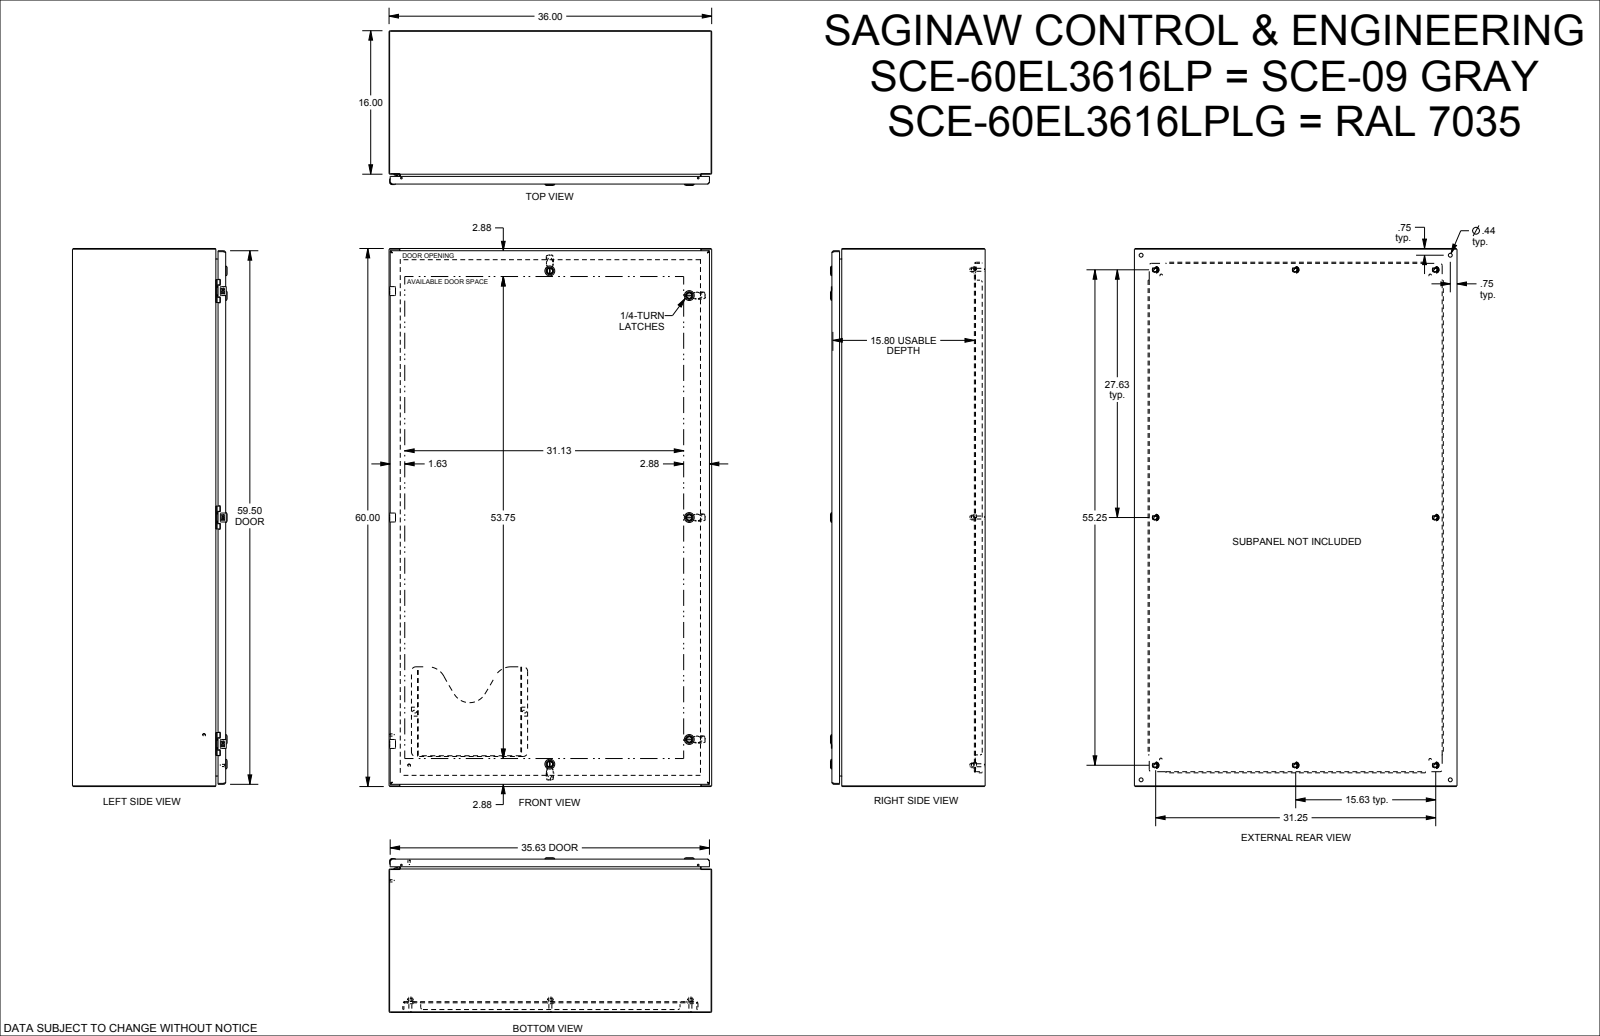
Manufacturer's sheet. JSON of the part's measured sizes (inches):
{"part_name": "SCE-60EL3616LP_REV2", "step_written_by": "SolidWorks 2021 (AUTOMOTIVE_DESIGN)", "units": "inches", "bodies": {"solids": 40, "faces": 2236, "planar": 1135, "cylindrical": 741, "other": 360}, "overall_size": [60, 36, 17.967], "volume_in3": 825.8, "surface_area_in2": 20194, "round_holes": [[0.5, 8], [0.172, 6], [0.205, 6], [0.244, 6], [0.375, 6], [0.197, 5], [0.394, 5], [0.634, 5], [0.281, 4], [0.437, 4], [0.04, 3], [0.218, 3]], "round_bosses_or_shafts": [[0.17, 9], [0.375, 8], [0.33, 8], [0.25, 6], [0.24, 6], [1.102, 5], [0.78, 5], [0.63, 5]], "partial_cylinders_radius": [[0.015, 28], [0.157, 20], [0.04, 17], [0.031, 14], [0.043, 12], [0.062, 12], [0.1, 12], [0.118, 12]], "face_to_face_distances": [0.075, 0.06, 17.097, 17.022, 17.037, 16.962, 35.925, 1.125, 1.075, 1], "hole_center_spacings": [25.25, 17.327, 15.625, 29.296, 31.738, 32.916, 44.004, 50.5]}
